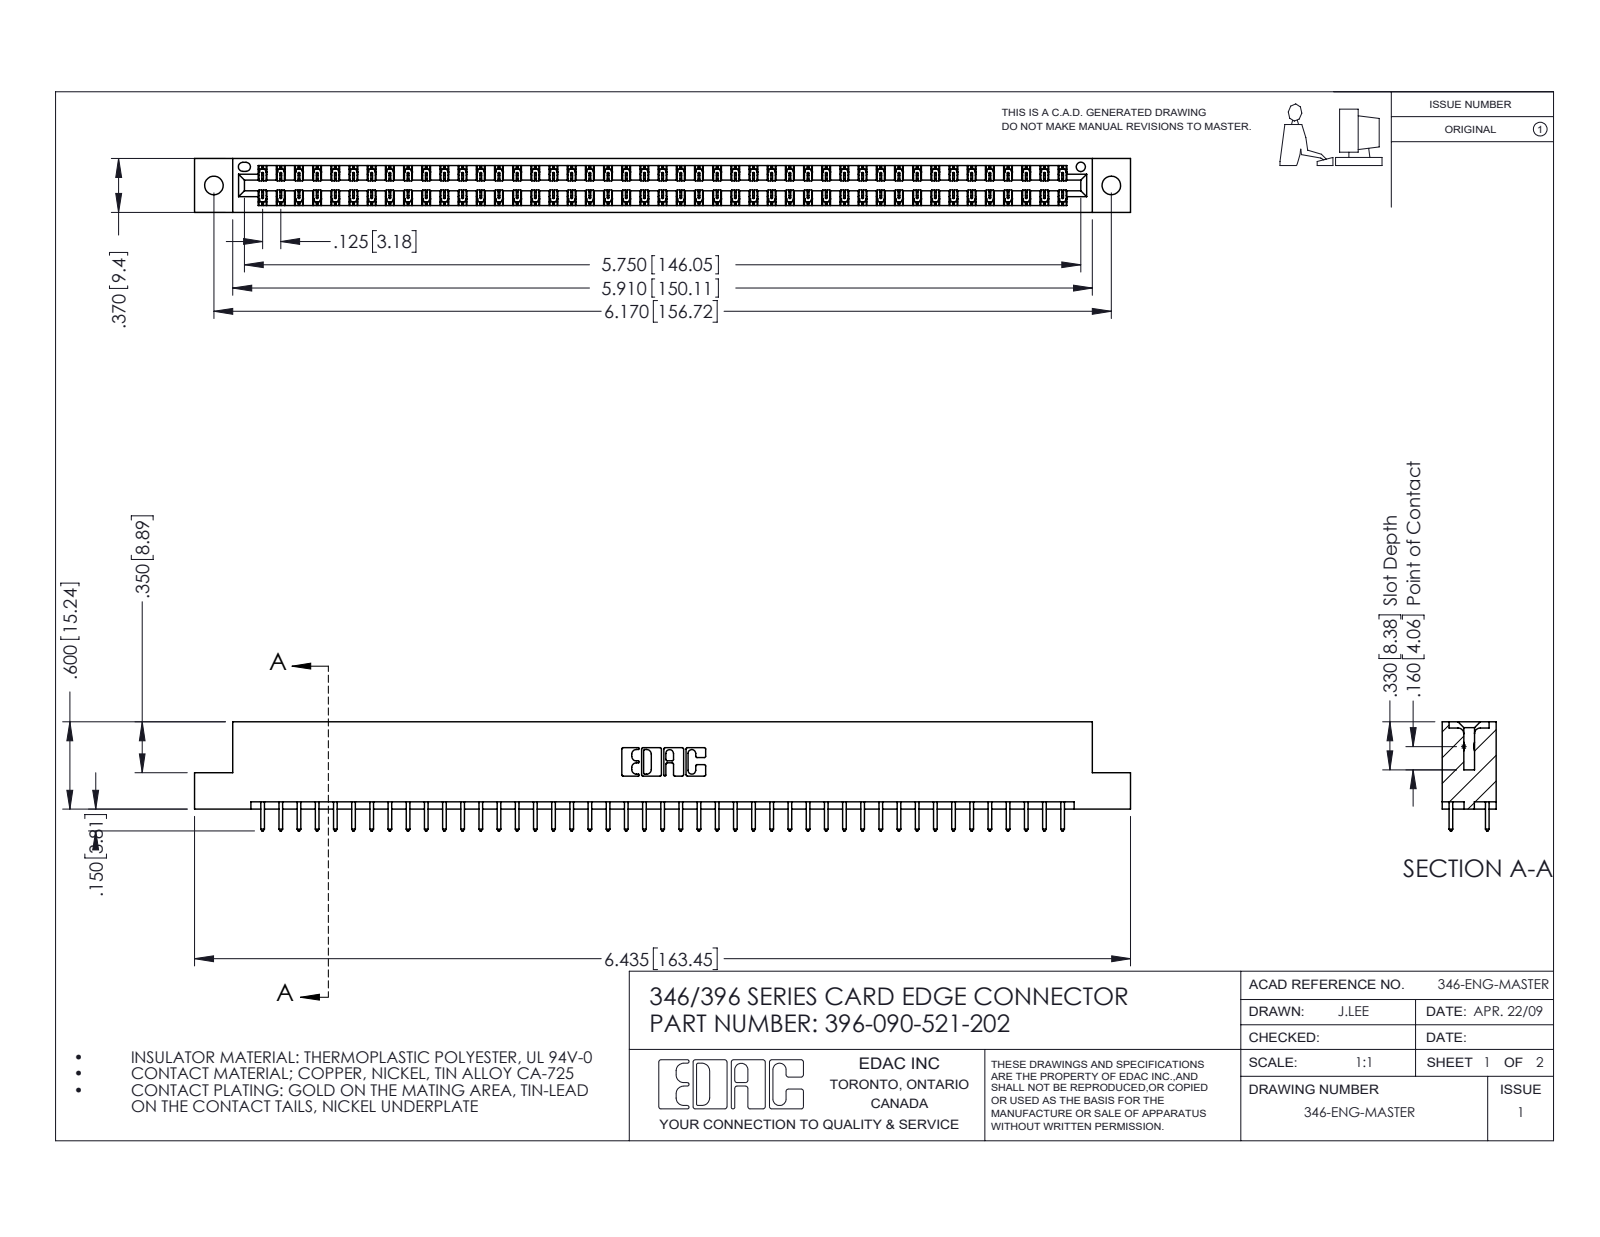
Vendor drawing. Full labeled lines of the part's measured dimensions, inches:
Part name (STEP PRODUCT): 346 Part_Flush Mounting Lugs - 0.128 Dia; 345-292-001_345-293-121; 396-090-521-202
STEP written by: SolidWorks 2016 (CONFIG_CONTROL_DESIGN)
Units: inches
Bodies: 91 solids, 4802 faces (3226 planar, 1576 cylindrical, 0 other)
Overall size (bounding box): 6.435 × 0.75 × 0.37
Volume: 0.97 in³ · Surface area: 33.12 in²
Round holes (diameter × count): ⌀0.128 ×2, ⌀0.064 ×1
Partial cylindrical surfaces — rounded edges, fillets, slot ends (radius × count): R0.006 ×135, R0.01 ×90, R0.01 ×22, R0.007 ×6, R0.031 ×6, R0.026 ×3, R0.014 ×2, R0.022 ×2
Main face-to-face distances: 0.048, 0.322, 0.25, 0.37, 0.072, 0.298, 0.025, 0.275, 0.148, 0.222
Hole centre spacings: 0.246, 5.961, 6.17
